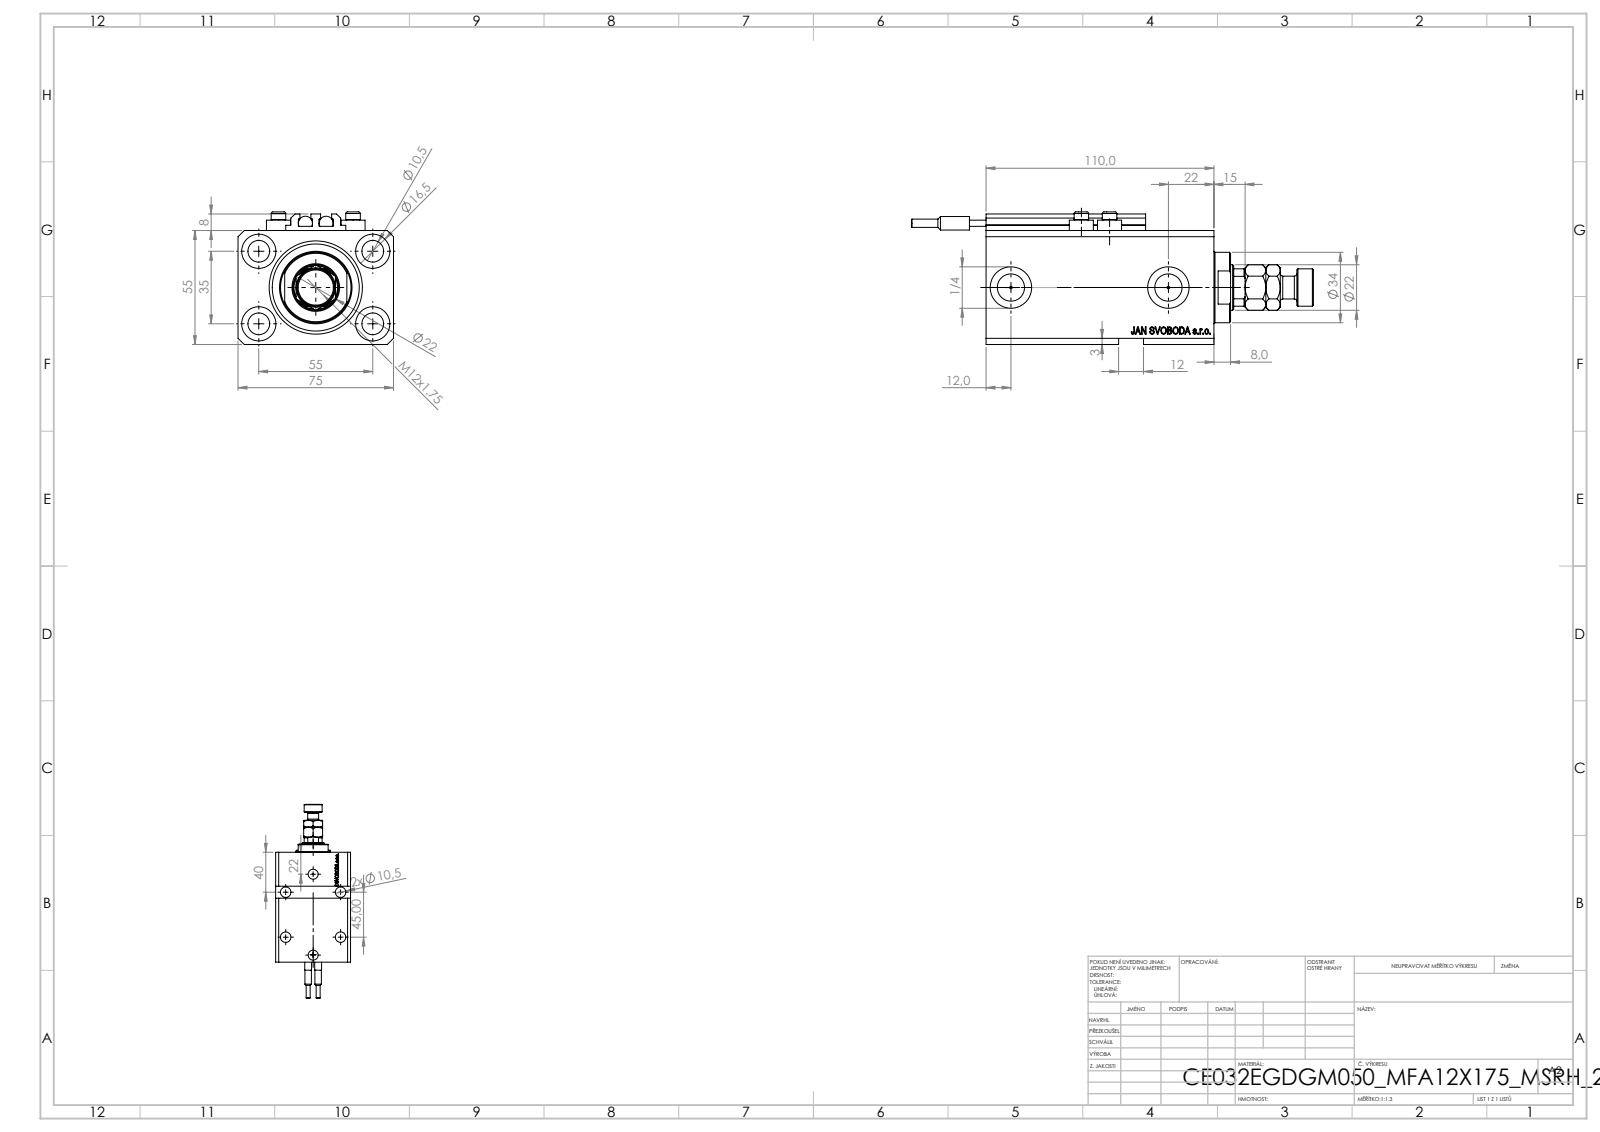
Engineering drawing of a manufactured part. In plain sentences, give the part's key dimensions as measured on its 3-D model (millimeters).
The part is named "ALLEN BOLT V250CE; V250CE_C_VCP; SWITCH_V250CE; MFA (+2 more)". Its 3-D file was written by "SolidWorks 2019 (CONFIG_CONTROL_DESIGN)". It is 11 solids with 1204 faces: 566 planar, 174 cylindrical and 464 other. Overall it measures 194 by 75 by 64 millimeters. Its volume is 389 358 cubic millimeters and its surface area 102 238 square millimeters. Round holes: 9 of diameter 10.5, 4 of diameter 1.25, 4 of diameter 4, 4 of diameter 16.5, 2 of diameter 10, 2 of diameter 13.16, 2 of diameter 20, 1 of diameter 22, 1 of diameter 32, 1 of diameter 45. Round bosses or shafts: 4 of diameter 11.6, 4 of diameter 7, 2 of diameter 6.8, 2 of diameter 6.5, 2 of diameter 4, 1 of diameter 34, 1 of diameter 18, 1 of diameter 11. Partial cylindrical surfaces (rounded edges, fillets, slot ends): 10 of radius 0.2, 1 of radius 10.5. The main face-to-face distances are 55, 75, 15, 3, 110, 57, 95, 9.9, 85.1, 100.1. The hole center spacings are 32.6, 32.87, 55, 68.74, 13.6, 14.09, 23.05, 25.81.
